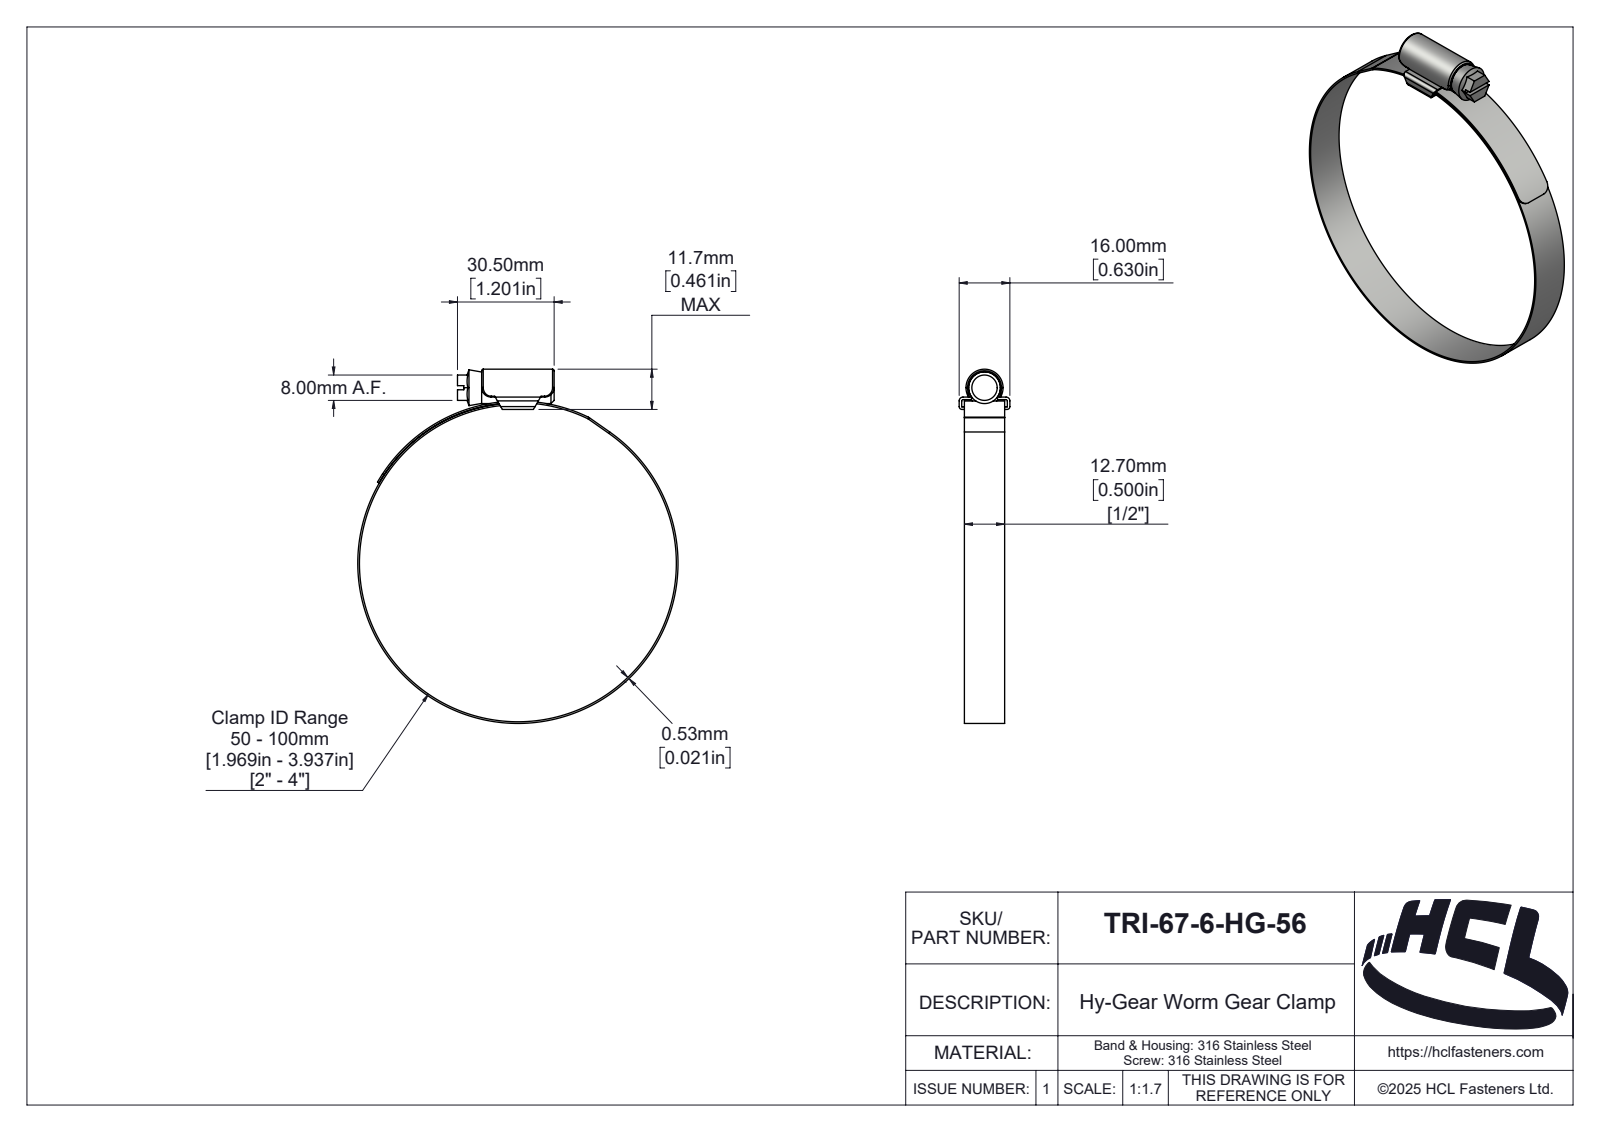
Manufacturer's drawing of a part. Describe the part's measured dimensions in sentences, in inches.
The part is named "TRI-57-0-HG-56". Its 3-D file was written by "SolidWorks 2025 (AUTOMOTIVE_DESIGN)". It is 3 solids with 189 faces: 39 planar, 89 cylindrical and 61 other. Overall it measures 4.399 by 3.979 by 0.63 inches. Its volume is 0.334 cubic inches and its surface area 19.65 square inches. Round holes: 1 of diameter 3.937. Round bosses or shafts: 1 of diameter 3.979, 1 of diameter 0.394. Partial cylindrical surfaces (rounded edges, fillets, slot ends): 6 of radius 0.02, 4 of radius 0.118, 2 of radius 0.004, 2 of radius 0.035, 2 of radius 0.047, 1 of radius 0.018, 1 of radius 0.074, 1 of radius 0.079. The main face-to-face distances are 0.031, 0.5, 0.122, 0.021, 0.091, 0.154, 1.201, 0.065, 0.565, 0.598.
